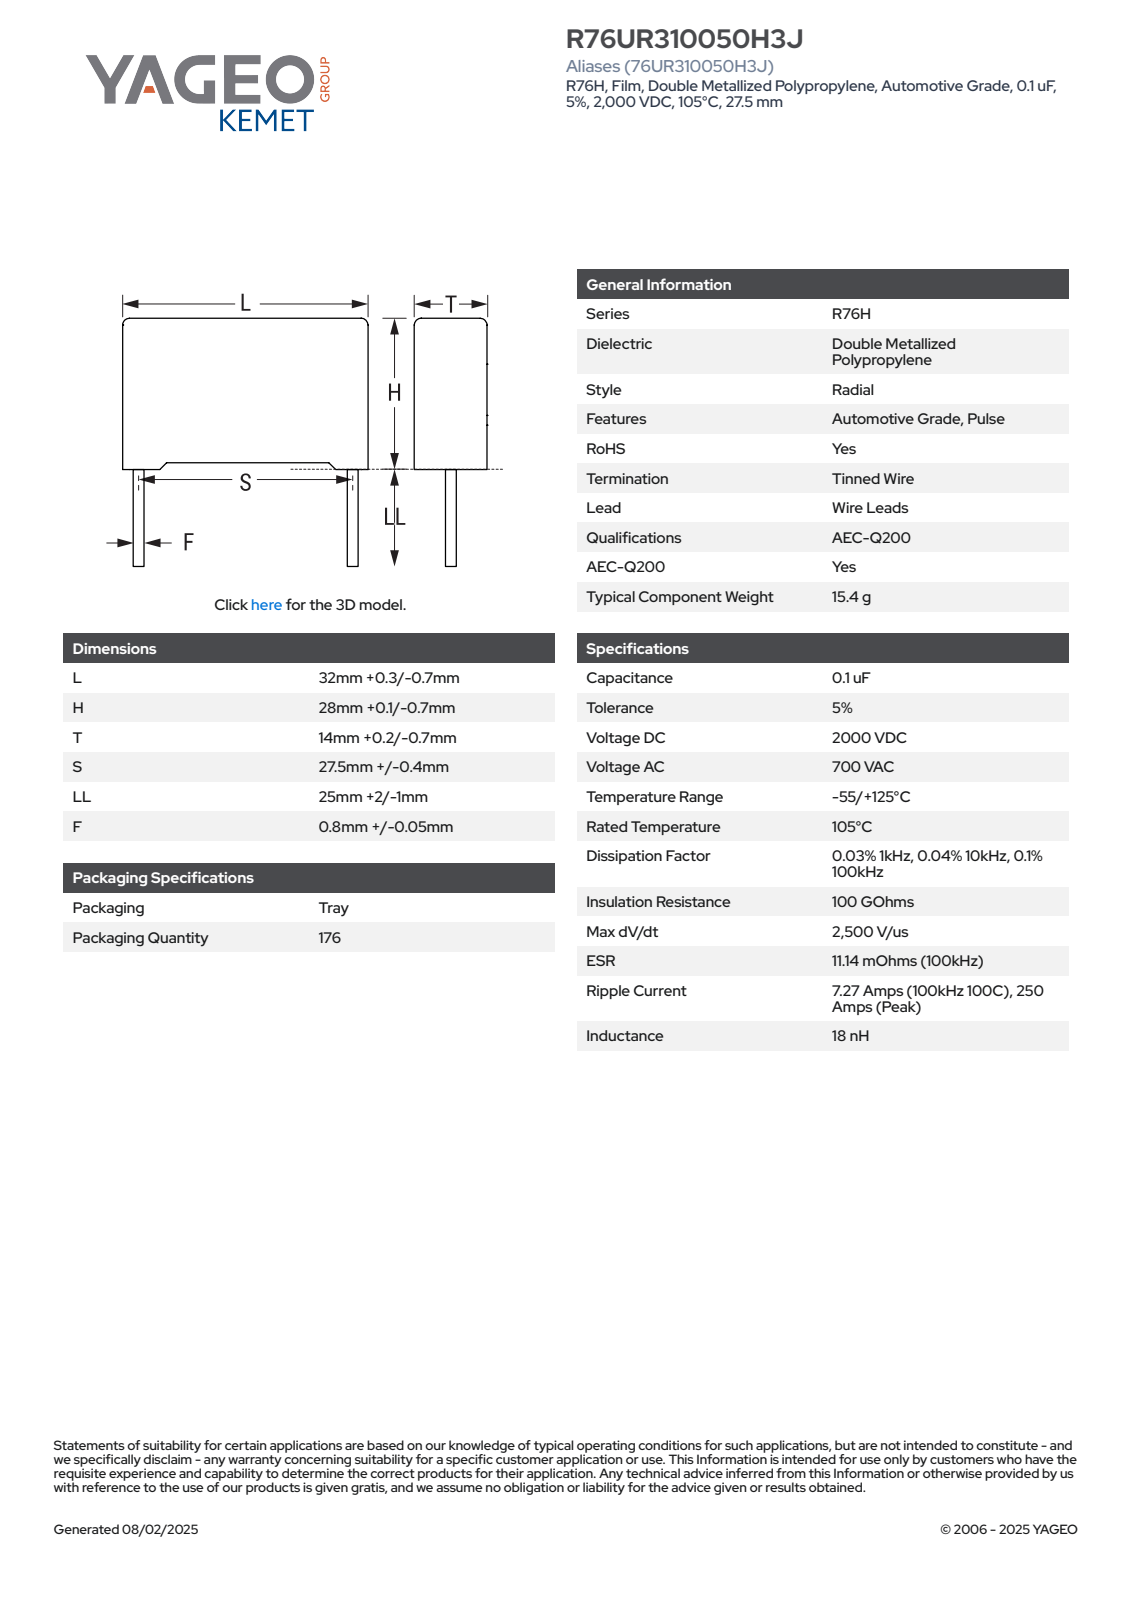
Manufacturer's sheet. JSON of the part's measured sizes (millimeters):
{"part_name": "CFR_RB2R76_32X28X14_L32.3H28.1T14.2S27.5LL27F0.85", "step_written_by": "SolidWorks 2014 (AUTOMOTIVE_DESIGN)", "units": "millimeters", "bodies": {"solids": 4, "faces": 85, "planar": 77, "cylindrical": 8, "other": 0}, "overall_size": [55.1, 32.3, 14.21], "volume_mm3": 12533, "surface_area_mm2": 3723, "round_bosses_or_shafts": [[0.85, 2]], "partial_cylinders_radius": [[0.5, 4]], "face_to_face_distances": [14.2, 32.3, 27.13, 27.35, 0.75, 0.97, 28.1, 1.08, 31.22, 13.12]}
